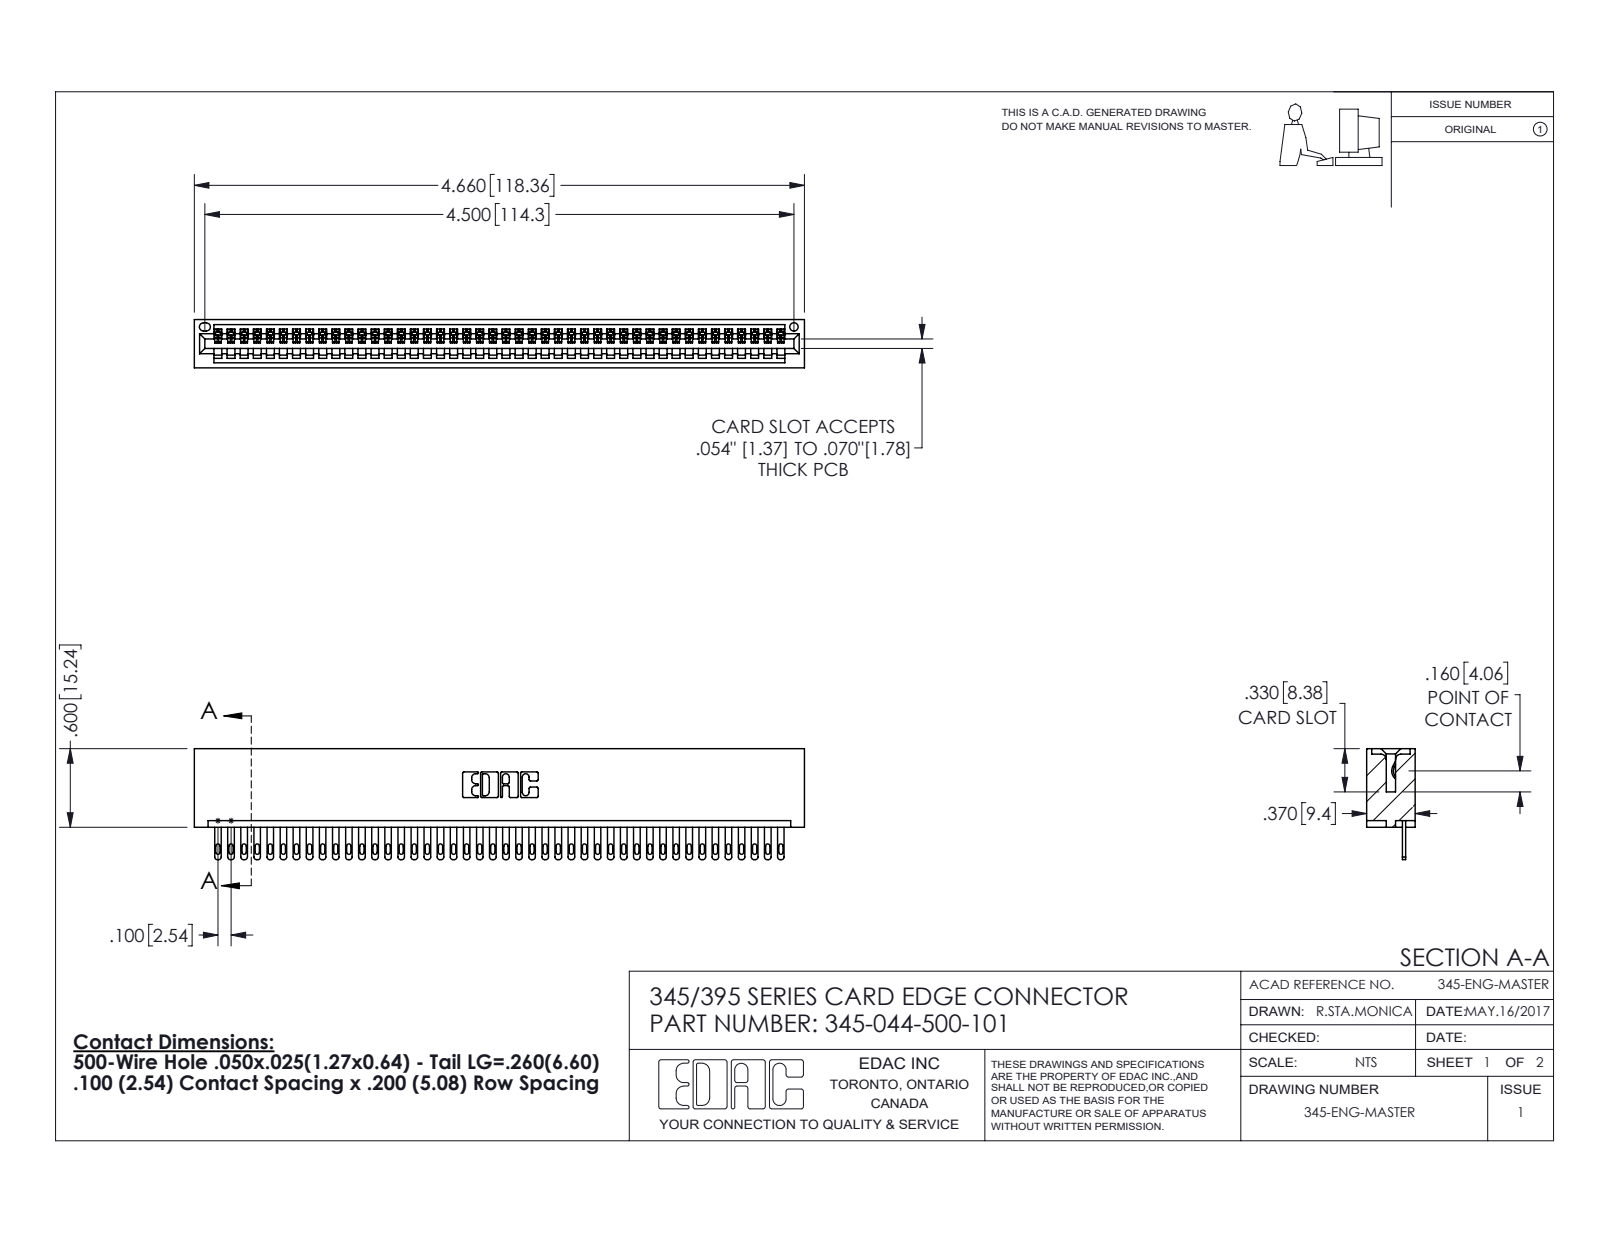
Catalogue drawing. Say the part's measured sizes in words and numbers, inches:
The part is named "345-292-001_345-293-100; 345 Part_No Mounting Lugs; 345-044-500-101". Its 3-D file was written by "SolidWorks 2016 (CONFIG_CONTROL_DESIGN)". It is 45 solids with 2494 faces: 1572 planar, 922 cylindrical and 0 other. Overall it measures 4.66 by 0.847 by 0.37 inches. Its volume is 0.724 cubic inches and its surface area 24.94 square inches. Round holes: 1 of diameter 0.064. Partial cylindrical surfaces (rounded edges, fillets, slot ends): 88 of radius 0.006, 88 of radius 0.016, 88 of radius 0.02, 22 of radius 0.01, 6 of radius 0.007, 6 of radius 0.031, 3 of radius 0.026, 2 of radius 0.031. The main face-to-face distances are 0.298, 0.072, 0.37, 0.098, 0.272, 0.025, 0.2, 0.225, 0.149, 0.072.
